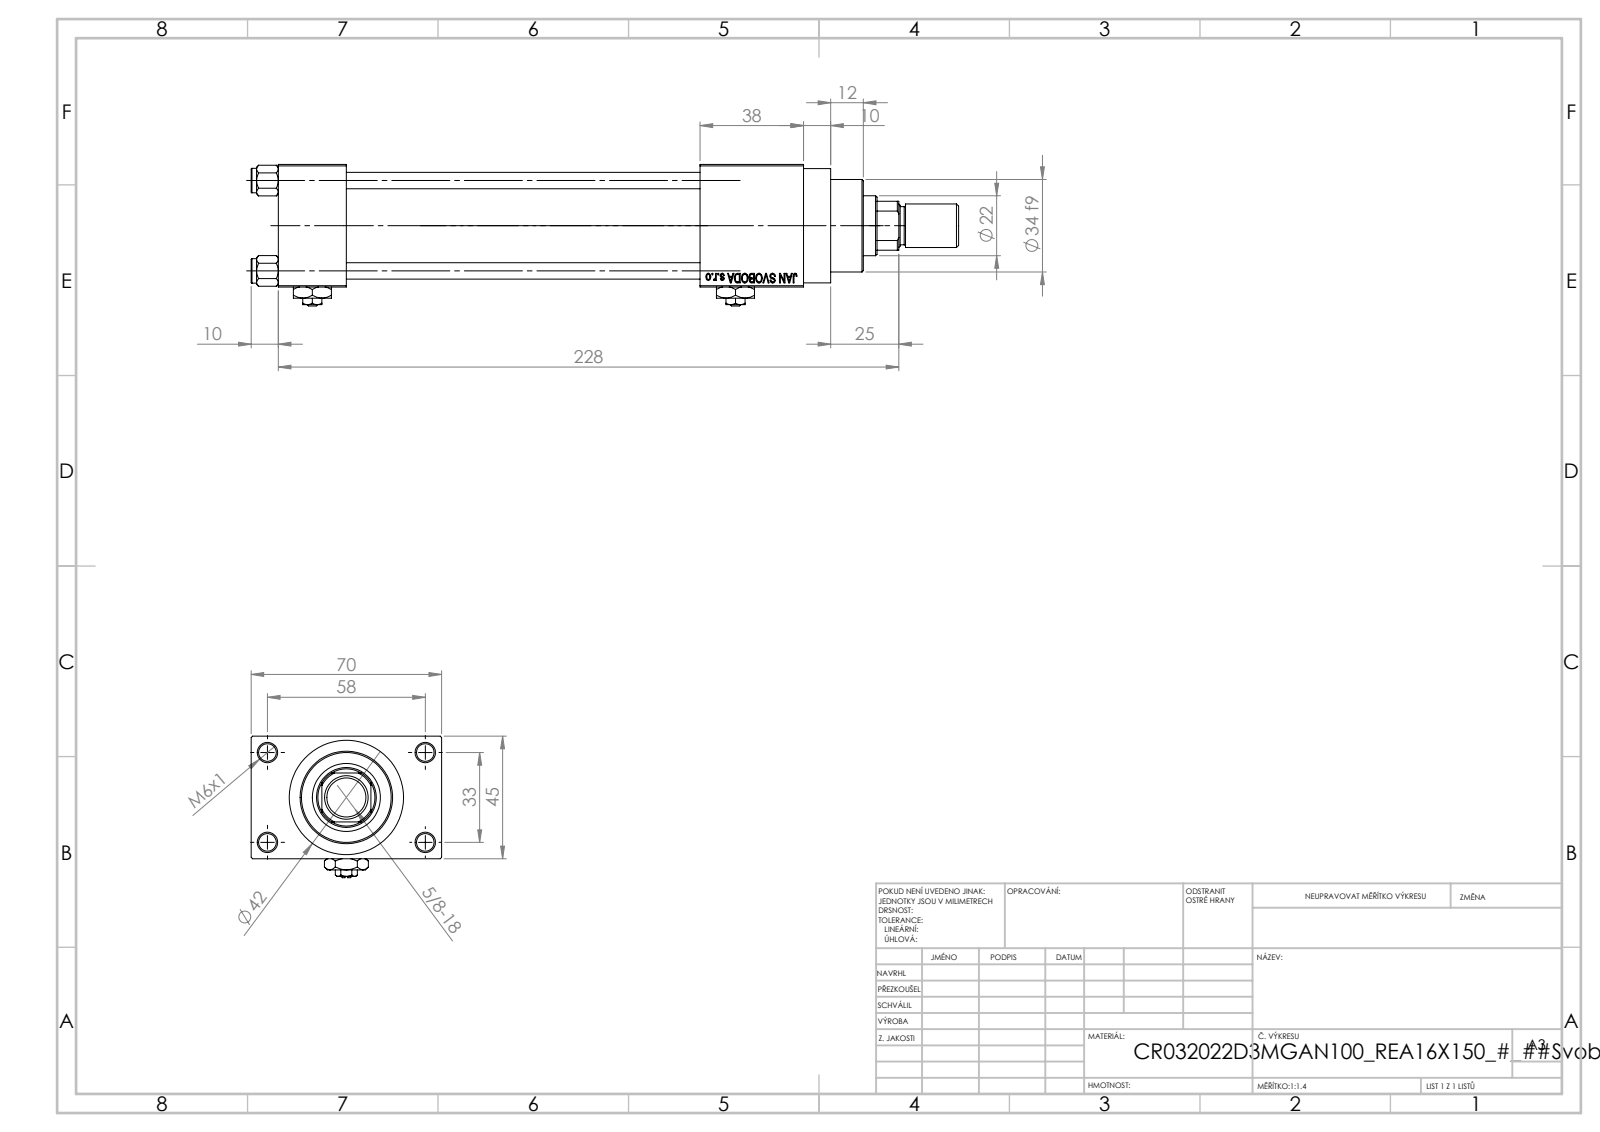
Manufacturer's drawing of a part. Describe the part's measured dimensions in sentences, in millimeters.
The part is named "ROD_END_AH; V215CR_D_Body; V215CR_VCP_D; NUT_M5_D (+3 more)". Its 3-D file was written by "SolidWorks 2019 (CONFIG_CONTROL_DESIGN)". It is 14 solids with 1216 faces: 546 planar, 104 cylindrical and 566 other. Overall it measures 260 by 70 by 52 millimeters. Its volume is 313 525 cubic millimeters and its surface area 111 895 square millimeters. Round holes: 4 of diameter 6, 4 of diameter 6.5, 2 of diameter 7, 2 of diameter 13.16, 2 of diameter 20, 1 of diameter 10.5, 1 of diameter 22, 1 of diameter 24, 1 of diameter 25, 1 of diameter 32, 1 of diameter 33. Round bosses or shafts: 4 of diameter 9, 1 of diameter 42, 1 of diameter 38, 1 of diameter 34, 1 of diameter 16, 1 of diameter 14. Partial cylindrical surfaces (rounded edges, fillets, slot ends): 1 of radius 10.5. The main face-to-face distances are 45, 25, 12.5, 57.5, 130, 155, 168, 38, 70, 193. The hole center spacings are 12.4, 23.48, 33.2, 33.37, 35.35, 45.6, 56.35, 33.
